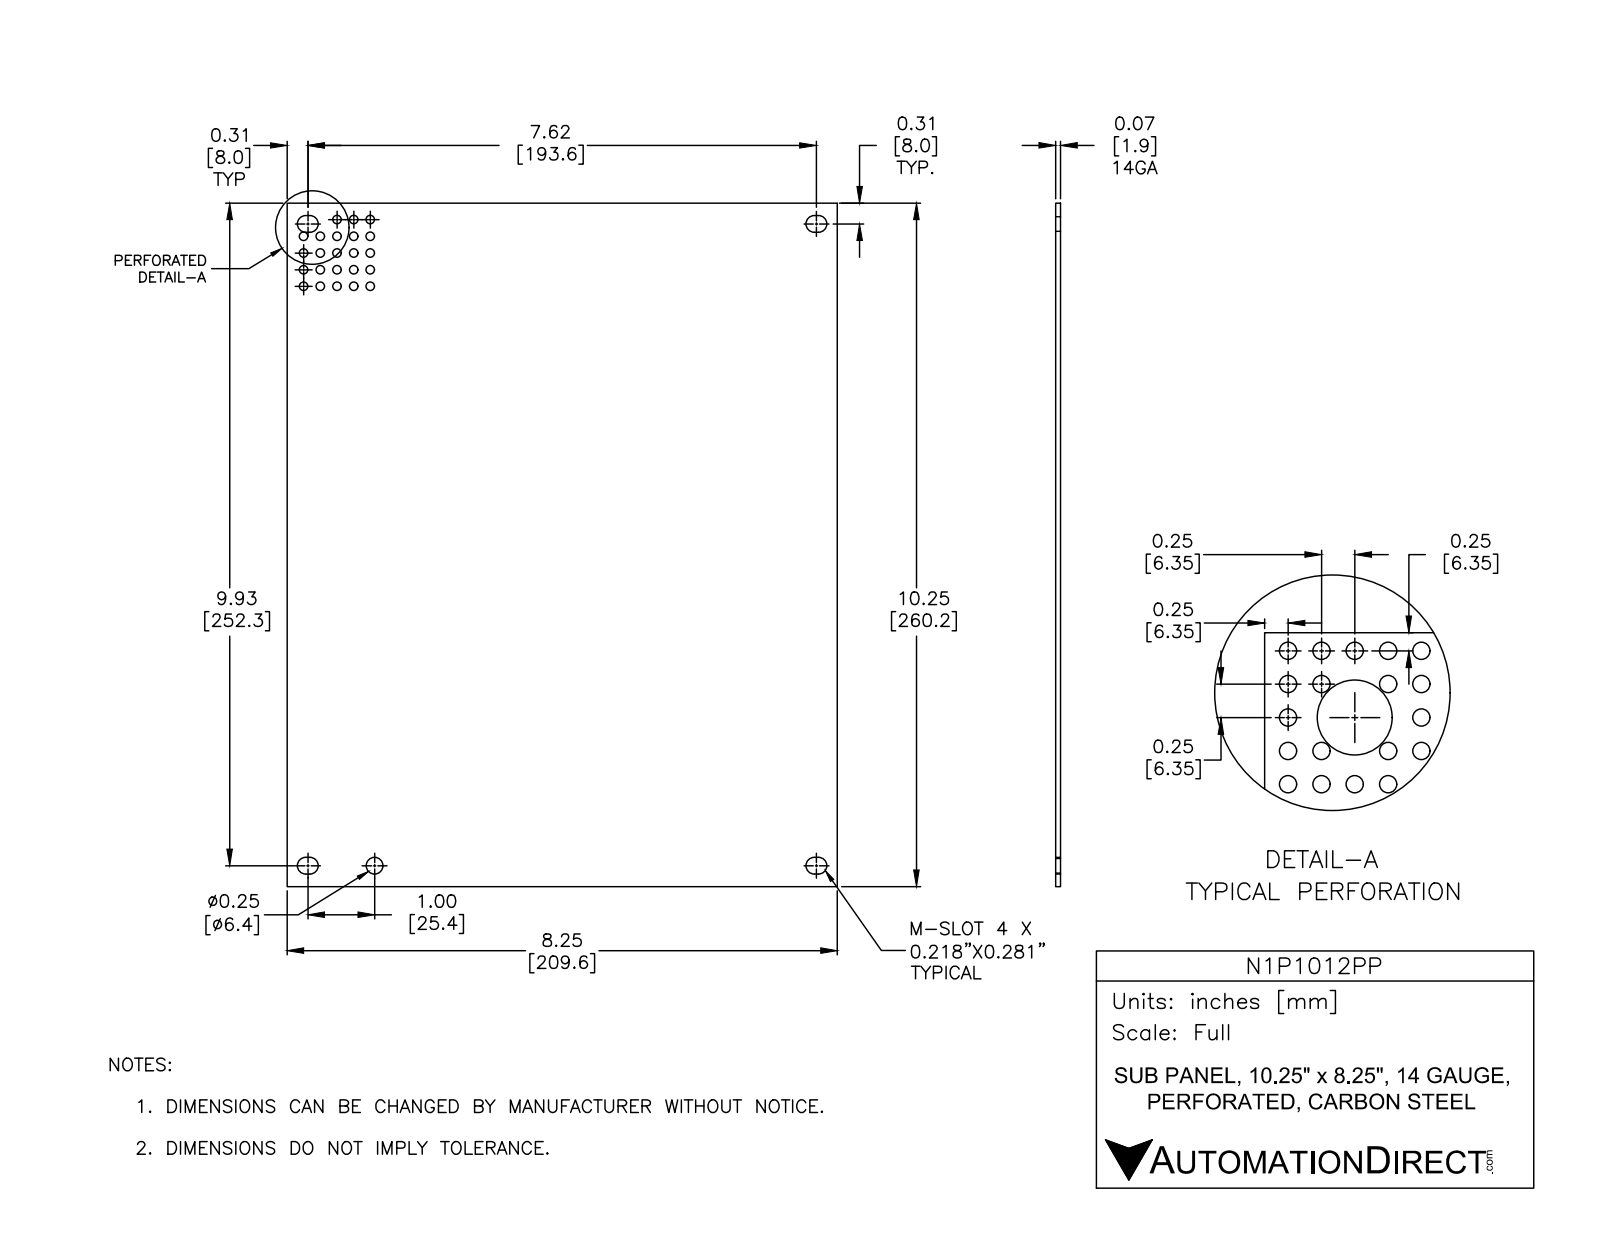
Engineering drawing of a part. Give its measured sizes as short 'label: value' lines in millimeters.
name: N1P1012PP
written by: Autodesk Inventor 2012 (AUTOMOTIVE_DESIGN)
unit: mm
bodies: 1 solid, 23 faces (14 planar, 9 cylindrical, 0 other)
size: 260.4 × 209.6 × 1.9
volume: 102 200 mm³; area: 110 700 mm²
holes: 1× ⌀6.4
rounds: 8× R3.2
face distances: 1.9, 209.6, 260.4, 4.8, 11.1, 249.2, 255.6, 244.4, 6.4, 250.8
